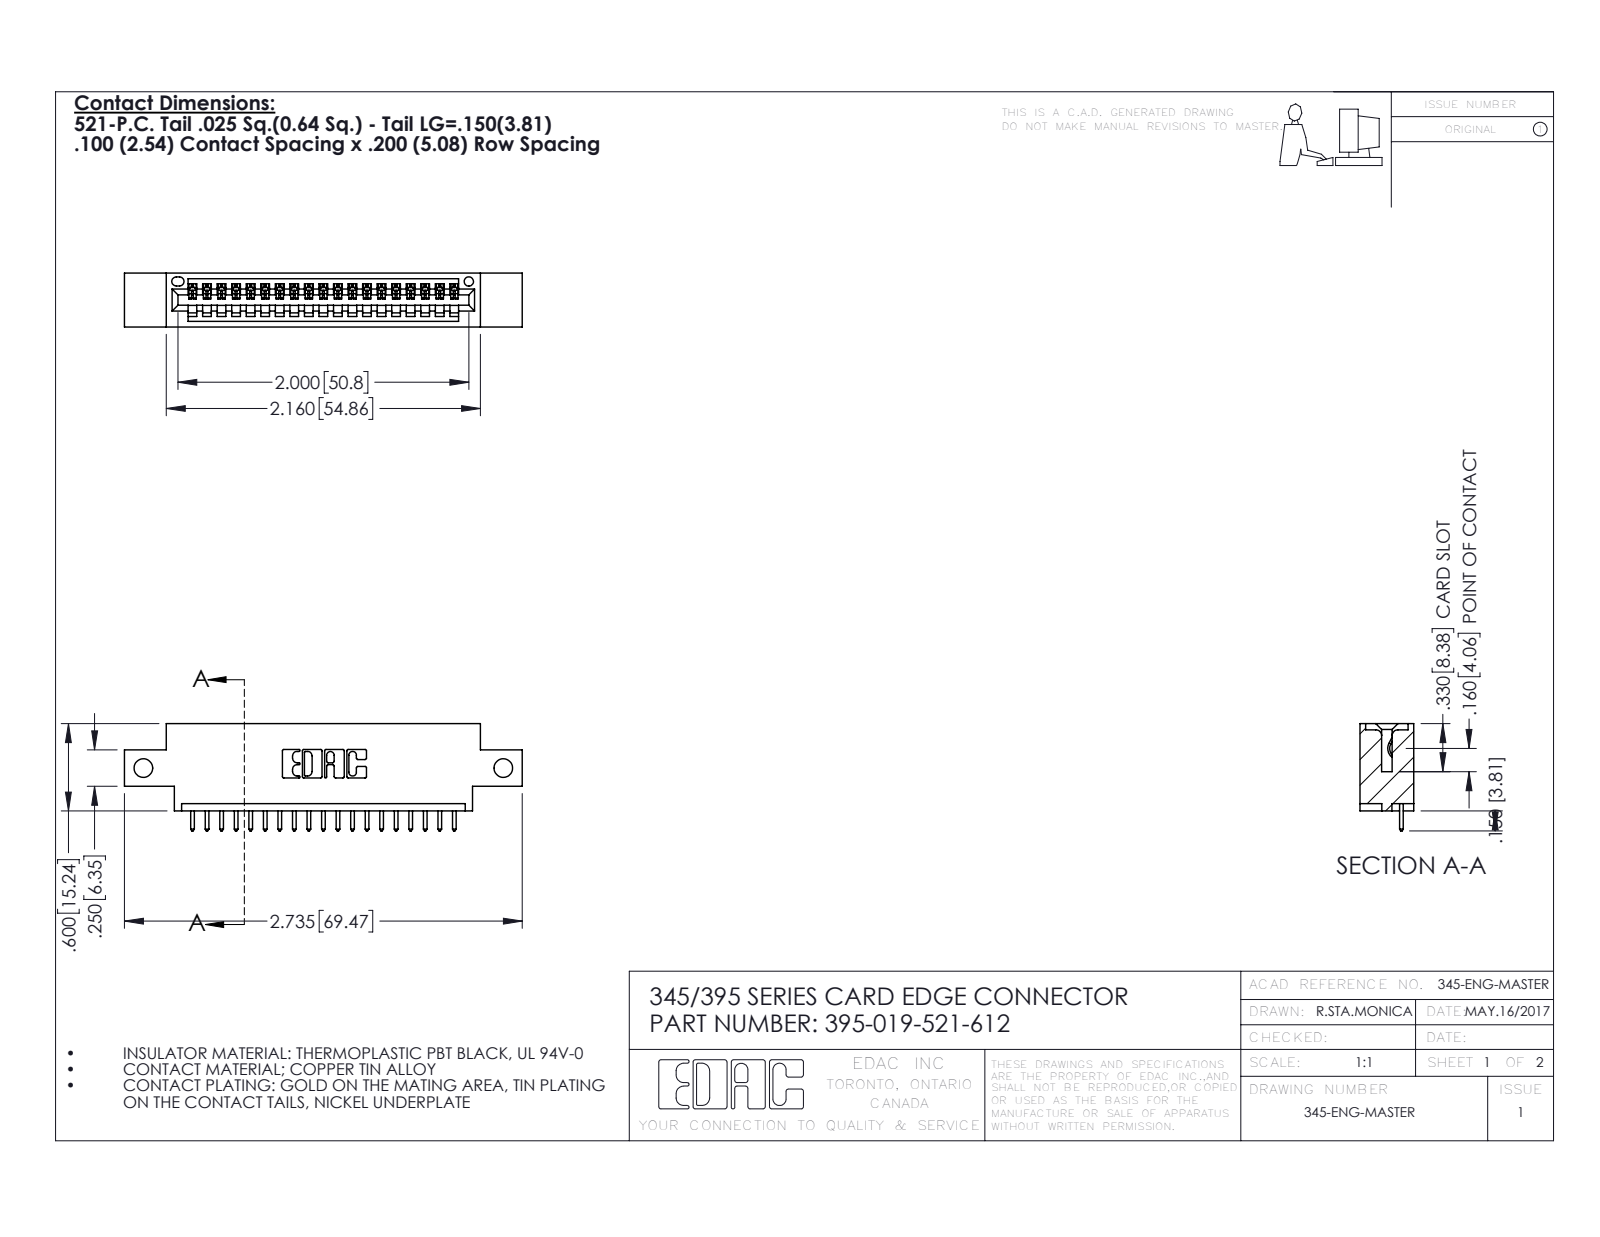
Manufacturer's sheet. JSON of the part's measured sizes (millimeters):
{"part_name": "345-292-001_345-293-121; 395-019-521-612; 345 Part_0.170 Offset - Side Mount", "step_written_by": "SolidWorks 2016 (CONFIG_CONTROL_DESIGN)", "units": "millimeters", "bodies": {"solids": 20, "faces": 1232, "planar": 844, "cylindrical": 388, "other": 0}, "overall_size": [69.5, 18.7, 9.4], "volume_mm3": 6160, "surface_area_mm2": 7639, "round_holes": [[3.3, 2], [1.6, 1]], "partial_cylinders_radius": [[0.2, 38], [0.3, 38], [0.3, 22], [0.2, 6], [0.8, 6], [0.7, 3], [0.8, 2], [1, 2]], "face_to_face_distances": [7.6, 1.8, 9.4, 5.1, 2.5, 6.9, 0.6, 5.7, 2.5, 3.8], "hole_center_spacings": [62.9]}
